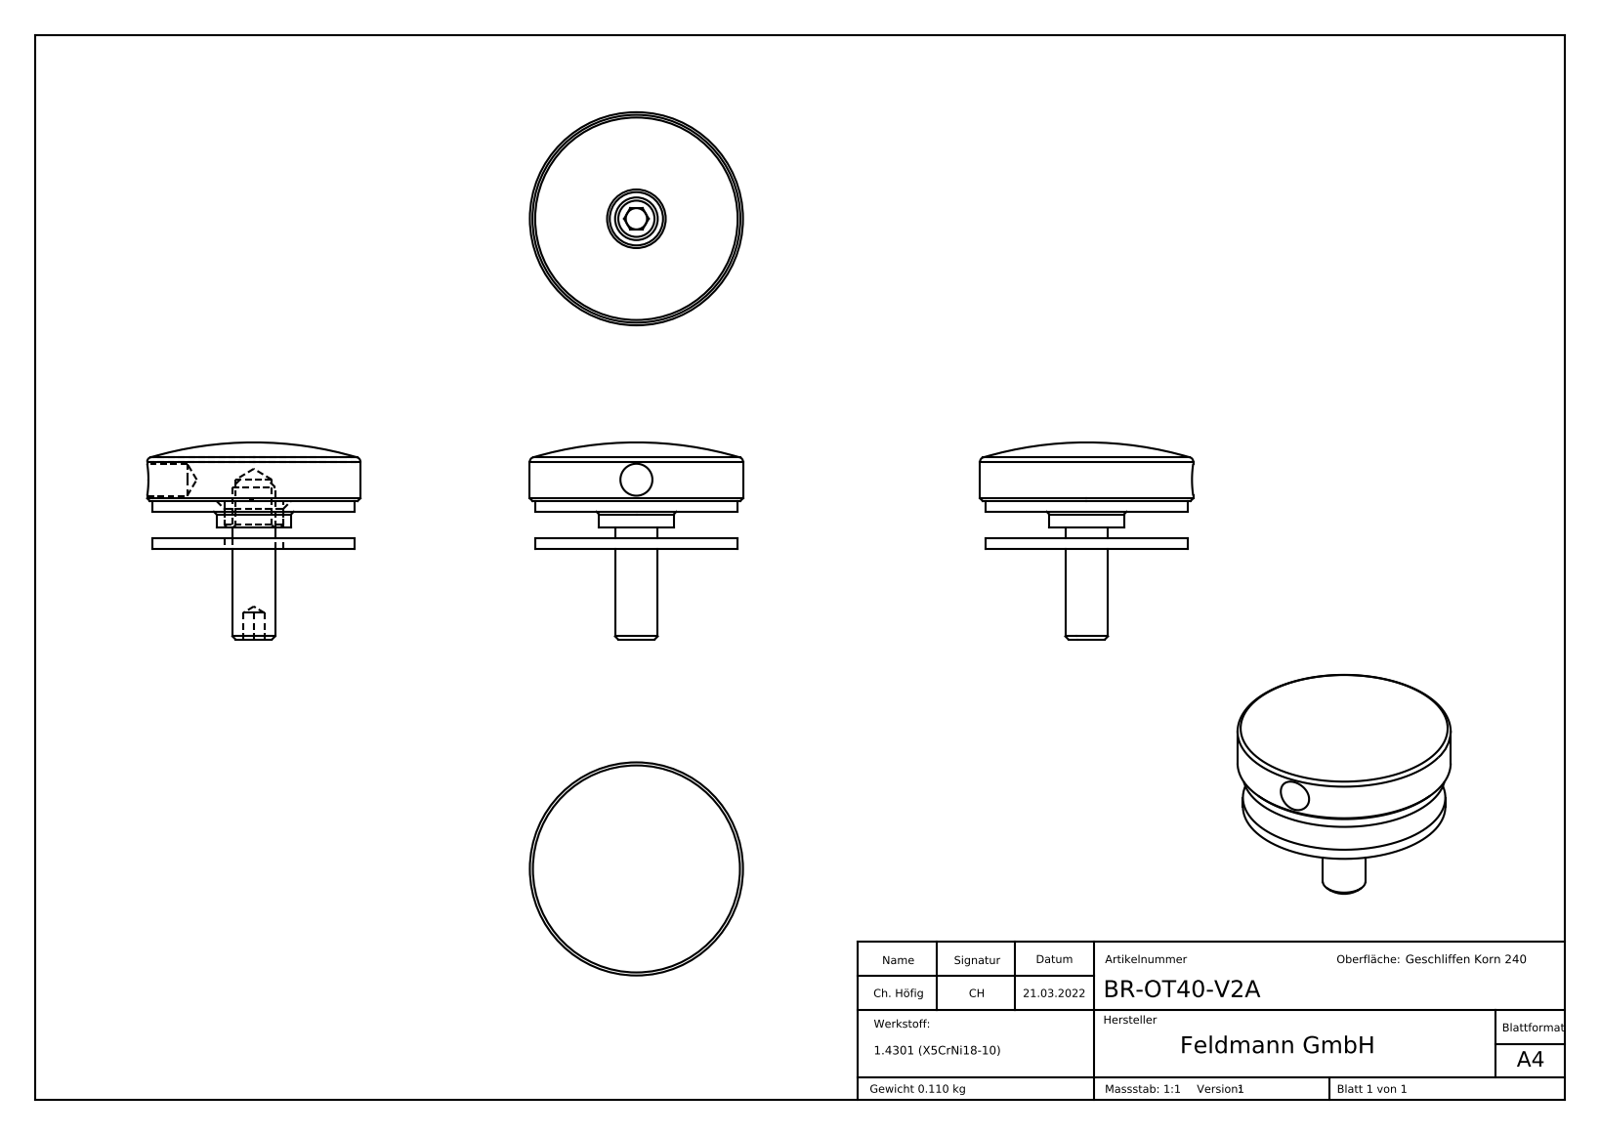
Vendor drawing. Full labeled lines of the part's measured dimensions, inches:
Part name (STEP PRODUCT): DIN913_DIN 913 M8x30; BR-OT40-V2A Teil4_BR-OT40-V2A Teil4; BR-OT40-V2A Teil1_BR-OT40-V2A Teil1; BR-OT40-V2A (+1 more)
STEP written by: SolidWorks 2018 (CONFIG_CONTROL_DESIGN)
Units: inches
Bodies: 4 solids, 284 faces (177 planar, 10 cylindrical, 97 other)
Overall size (bounding box): 1.575 × 1.575 × 1.457
Volume: 1.069 in³ · Surface area: 15.28 in²
Round holes (diameter × count): ⌀0.236 ×1, ⌀0.268 ×1, ⌀0.433 ×1
Round bosses / shafts (diameter × count): ⌀1.575 ×1, ⌀1.496 ×1, ⌀0.551 ×1, ⌀0.315 ×1
Main face-to-face distances: 0.079, 0.276, 0.354, 0.197, 0.157, 0.118, 0.748, 0.827, 0.669, 0.945
